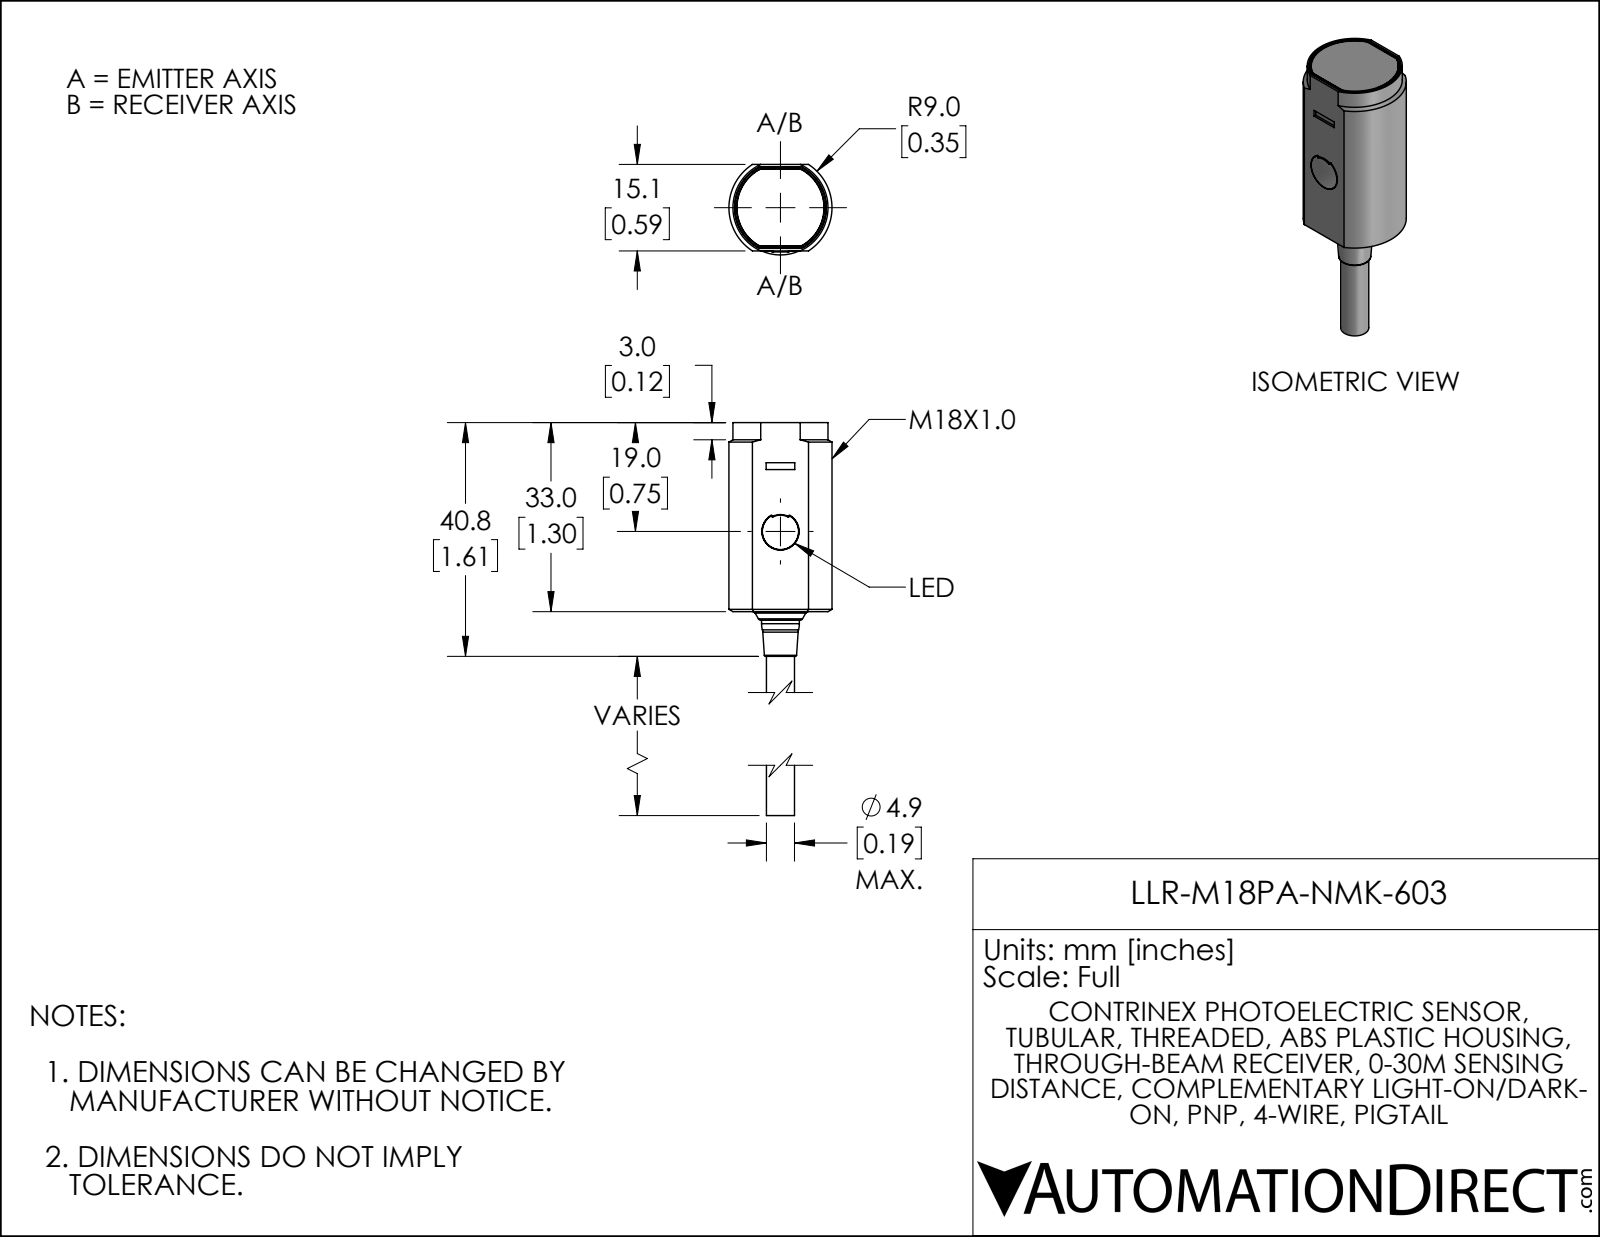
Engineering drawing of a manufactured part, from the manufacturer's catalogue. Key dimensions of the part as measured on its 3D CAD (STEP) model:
Part name (STEP PRODUCT): LLR-M18PA-NMK-603
STEP written by: SolidWorks 2021 (AUTOMOTIVE_DESIGN)
Units: inches
Bodies: 1 solid, 93 faces (39 planar, 41 cylindrical, 13 other)
Overall size (bounding box): 2.205 × 0.709 × 0.622
Volume: 0.501 in³ · Surface area: 4.23 in²
Round holes (diameter × count): ⌀0.256 ×1
Round bosses / shafts (diameter × count): ⌀0.26 ×1, ⌀0.193 ×1
Partial cylindrical surfaces — rounded edges, fillets, slot ends (radius × count): R0.006 ×8, R0.014 ×8, R0.028 ×8, R0.112 ×1, R0.116 ×1, R0.299 ×1, R0.302 ×1, R0.313 ×1
Main face-to-face distances: 0.594, 1.297, 1.299, 0.016, 2.205, 2.203, 0.906, 0.579, 0.014, 0.563
